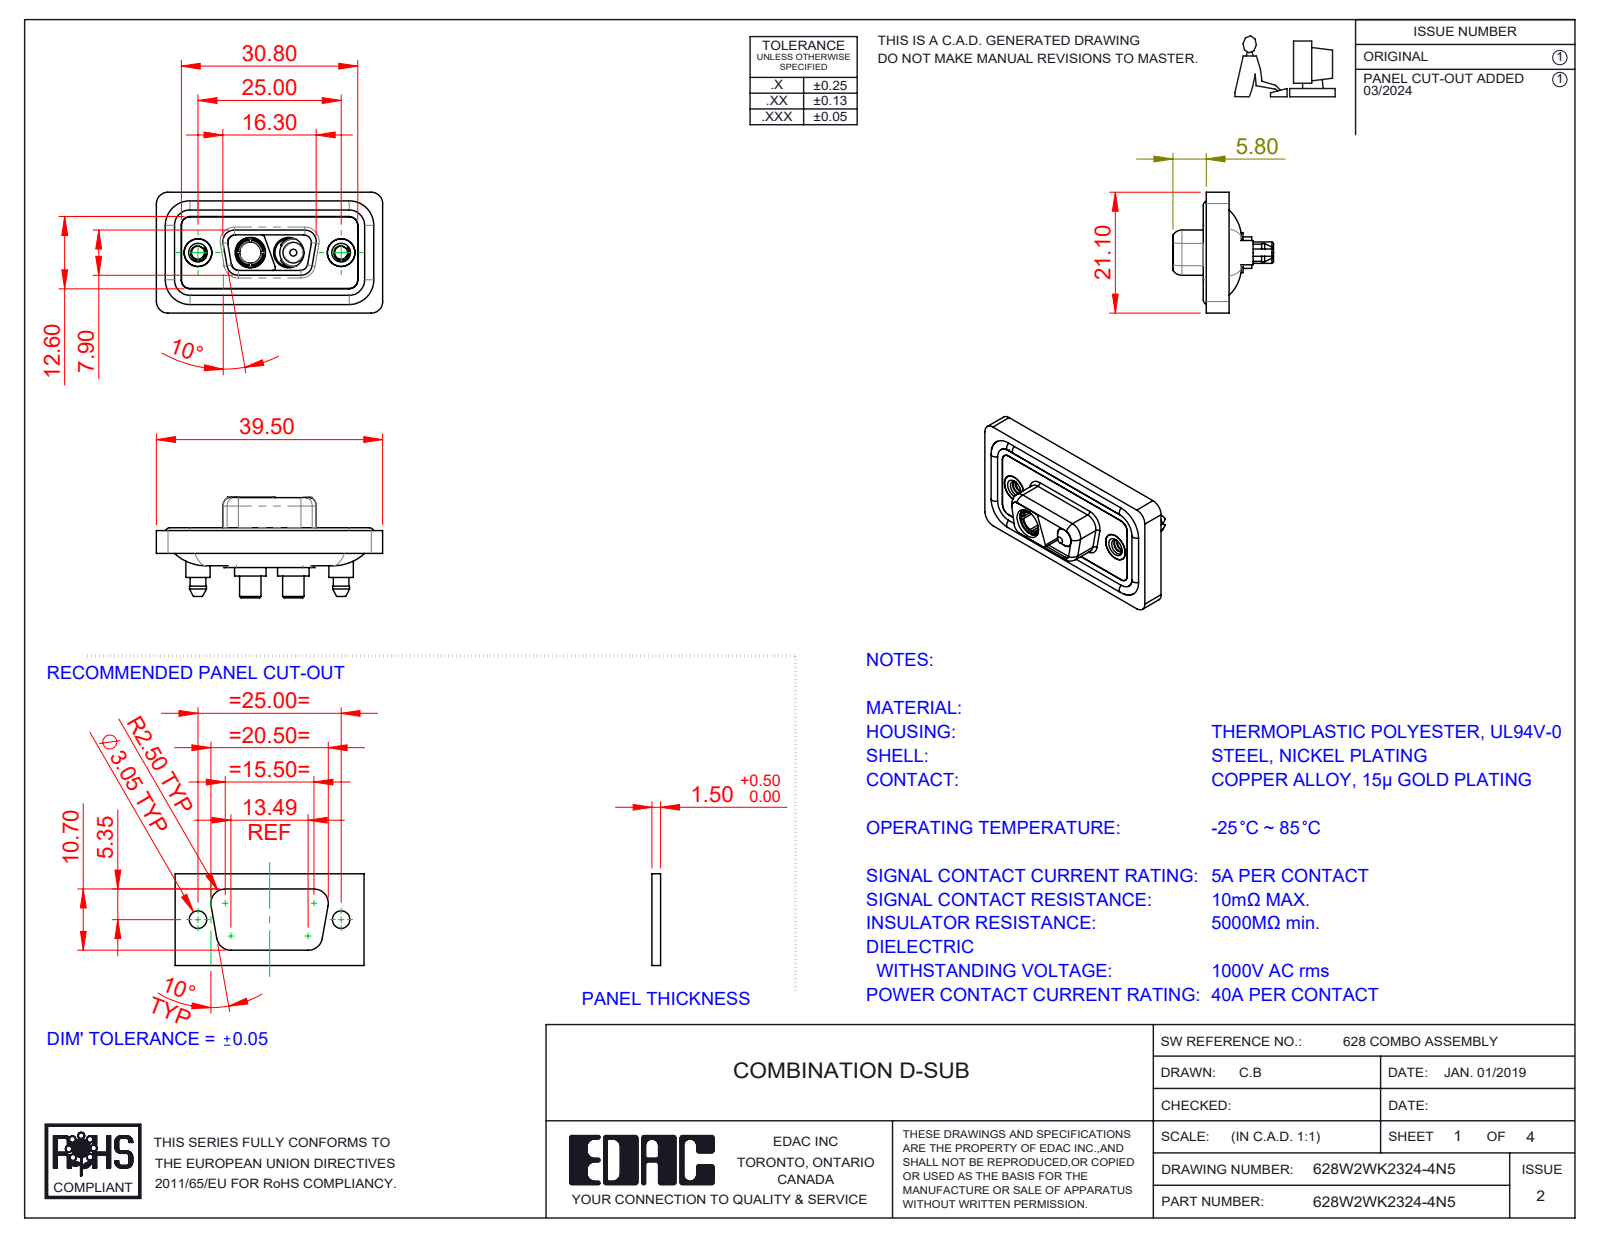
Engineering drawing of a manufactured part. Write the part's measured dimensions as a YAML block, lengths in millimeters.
part_name: "628Combo Shell Rear_09 Contacts; 628Combo Threaded Boardlock_5; 628W2WK2324-4N5; 628Combo Shell Front_09 Contacts (+4 more)"
step_written_by: "SolidWorks 2023 (CONFIG_CONTROL_DESIGN)"
units: millimeters
bodies: {solids: 11, faces: 550, planar: 160, cylindrical: 263, other: 127}
overall_size: [39.5, 21.1, 17.55]
volume: 4774
surface_area: 7698
round_holes:
  - {diameter: 4.85, count: 4}
  - {diameter: 2.26, count: 2}
  - {diameter: 4, count: 2}
  - {diameter: 4.05, count: 2}
  - {diameter: 5, count: 2}
  - {diameter: 5.3, count: 2}
  - {diameter: 3.7, count: 1}
round_bosses_or_shafts:
  - {diameter: 1.6, count: 4}
  - {diameter: 5.5, count: 2}
  - {diameter: 5.4, count: 2}
  - {diameter: 5.2, count: 2}
  - {diameter: 4.95, count: 2}
  - {diameter: 4.8, count: 2}
  - {diameter: 4.75, count: 2}
  - {diameter: 4.25, count: 2}
partial_cylinders:
  - {radius: 1.5, count: 24}
  - {radius: 2, count: 18}
  - {radius: 1.6, count: 10}
  - {radius: 1.35, count: 8}
  - {radius: 0.5, count: 6}
  - {radius: 0.25, count: 4}
  - {radius: 0.6, count: 4}
  - {radius: 0.65, count: 4}
face_to_face_distances: [0.4, 1.1, 2.9, 1.6, 0.5, 1.8, 5.65, 4, 1.5, 5.35]
hole_center_spacings: [9.14, 15.86, 6.72, 25]
